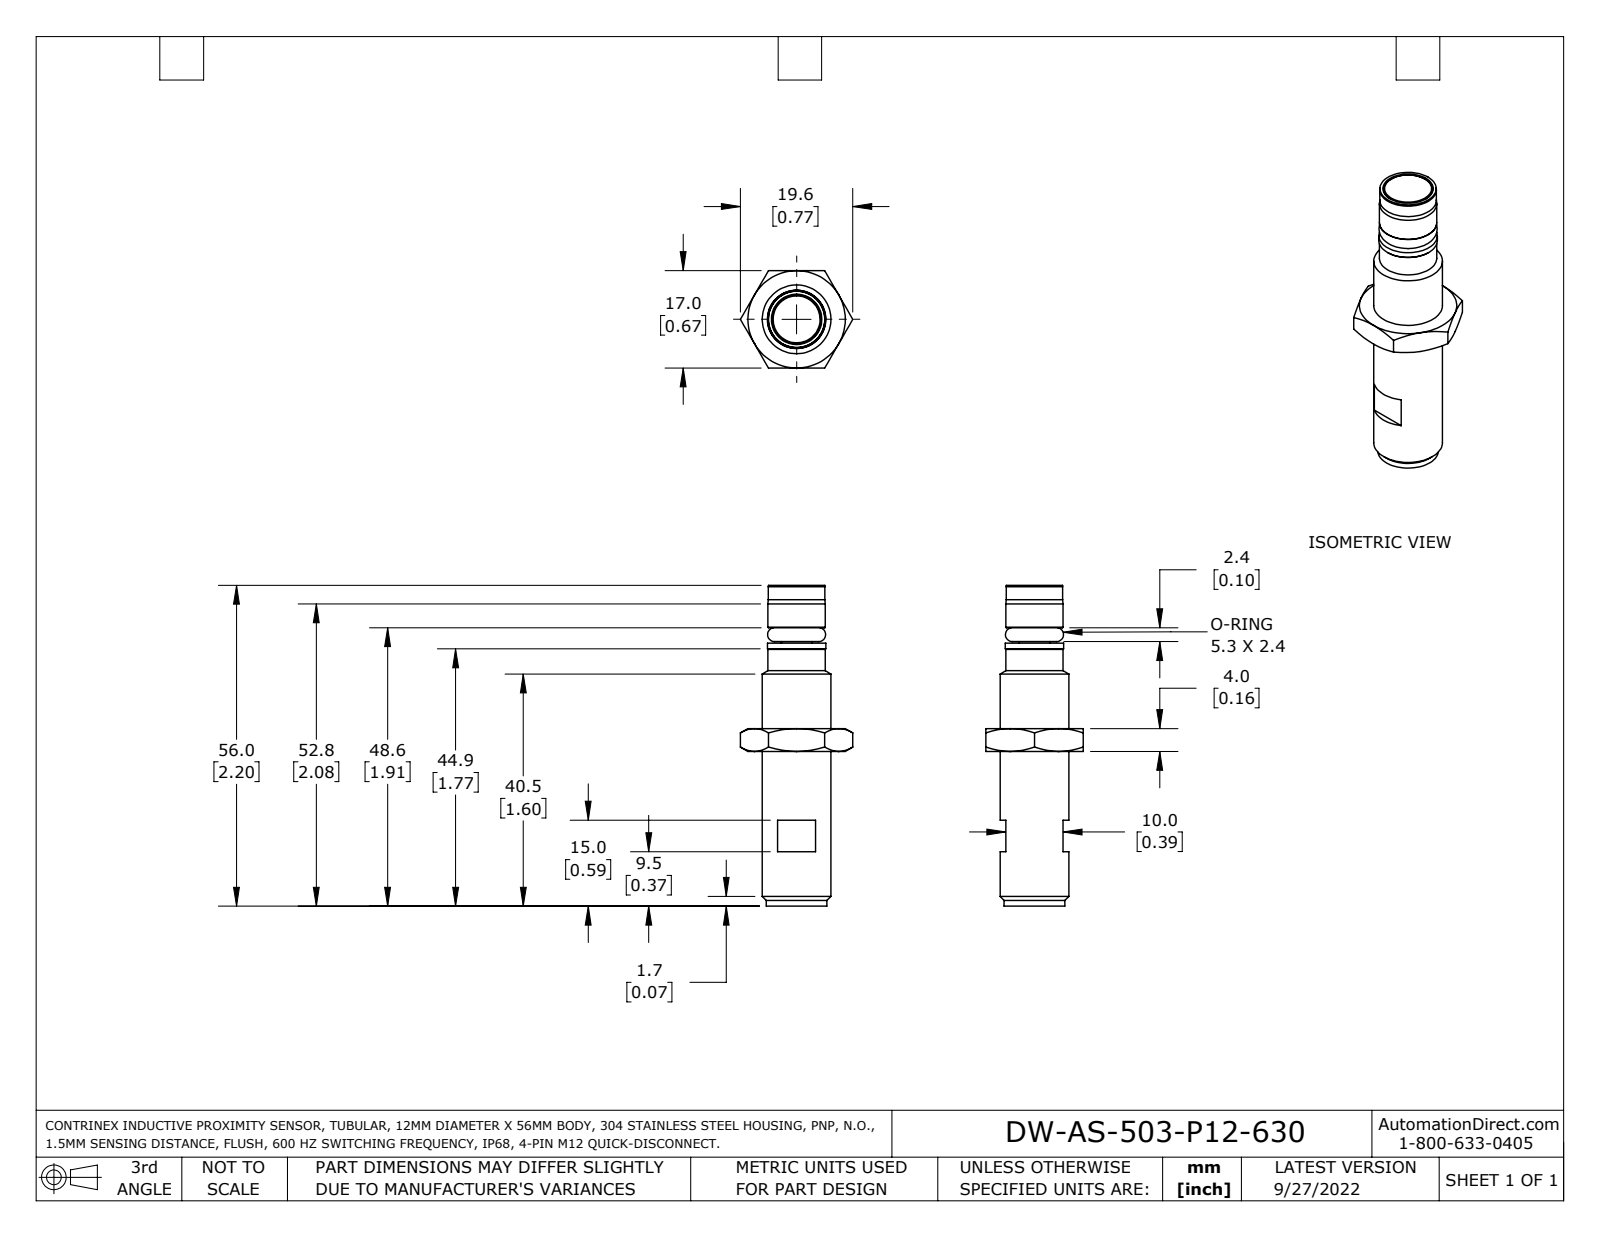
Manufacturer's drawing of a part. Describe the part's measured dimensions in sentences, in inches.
The part is named "DW-AS-503-P12-630". Its 3-D file was written by "SolidWorks 2021 (AUTOMOTIVE_DESIGN)". It is 1 solid with 87 faces: 41 planar, 21 cylindrical and 25 other. Overall it measures 2.205 by 0.773 by 0.669 inches. Its volume is 0.35 cubic inches and its surface area 4.833 square inches. Round holes: 1 of diameter 0.236, 1 of diameter 0.331. Round bosses or shafts: 4 of diameter 0.039, 1 of diameter 0.472, 1 of diameter 0.417, 1 of diameter 0.402, 1 of diameter 0.394, 1 of diameter 0.389, 1 of diameter 0.209. Partial cylindrical surfaces (rounded edges, fillets, slot ends): 4 of radius 0.049, 2 of radius 0.008, 1 of radius 0.02. The main face-to-face distances are 0.669, 0.157, 0.138, 0.531, 0.984, 1.142, 0.398, 0.587, 0.744, 0.394.
